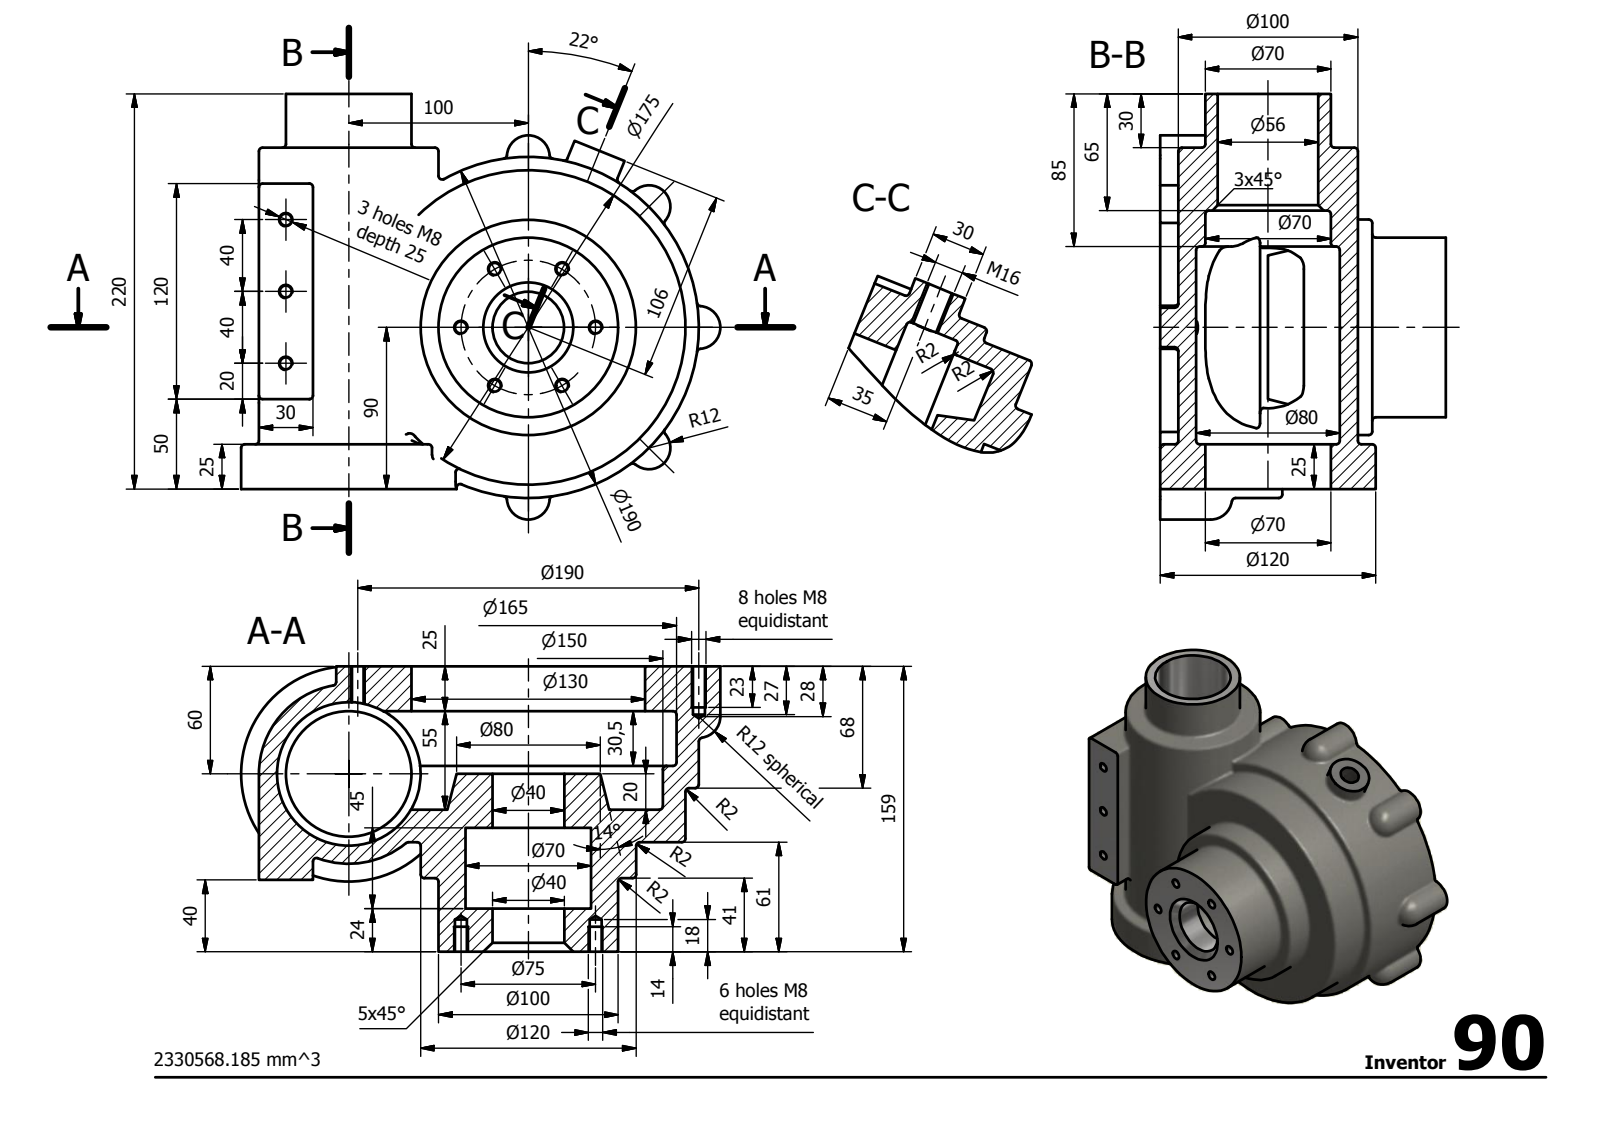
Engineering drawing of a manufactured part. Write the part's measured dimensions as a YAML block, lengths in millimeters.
step_written_by: "Autodesk Inventor 2014 (AUTOMOTIVE_DESIGN)"
units: millimeters
bodies: {solids: 1, faces: 167, planar: 24, cylindrical: 66, other: 77}
overall_size: [267, 237, 159]
volume: 2331000
surface_area: 315398
round_holes:
  - {diameter: 6.65, count: 17}
  - {diameter: 70, count: 2}
  - {diameter: 13.84, count: 1}
  - {diameter: 40, count: 1}
  - {diameter: 56, count: 1}
  - {diameter: 80, count: 1}
  - {diameter: 130, count: 1}
  - {diameter: 150, count: 1}
  - {diameter: 165, count: 1}
round_bosses_or_shafts:
  - {diameter: 120, count: 2}
  - {diameter: 100, count: 2}
  - {diameter: 190, count: 1}
  - {diameter: 30, count: 1}
partial_cylinders:
  - {radius: 2, count: 19}
  - {radius: 12, count: 8}
  - {radius: 87.5, count: 1}
face_to_face_distances: [80, 55, 25, 18, 98, 73, 20, 30, 38, 61]
hole_center_spacings: [37.5, 72.71, 175.54, 59.58, 64.95, 65.27, 73.44, 82.88]
